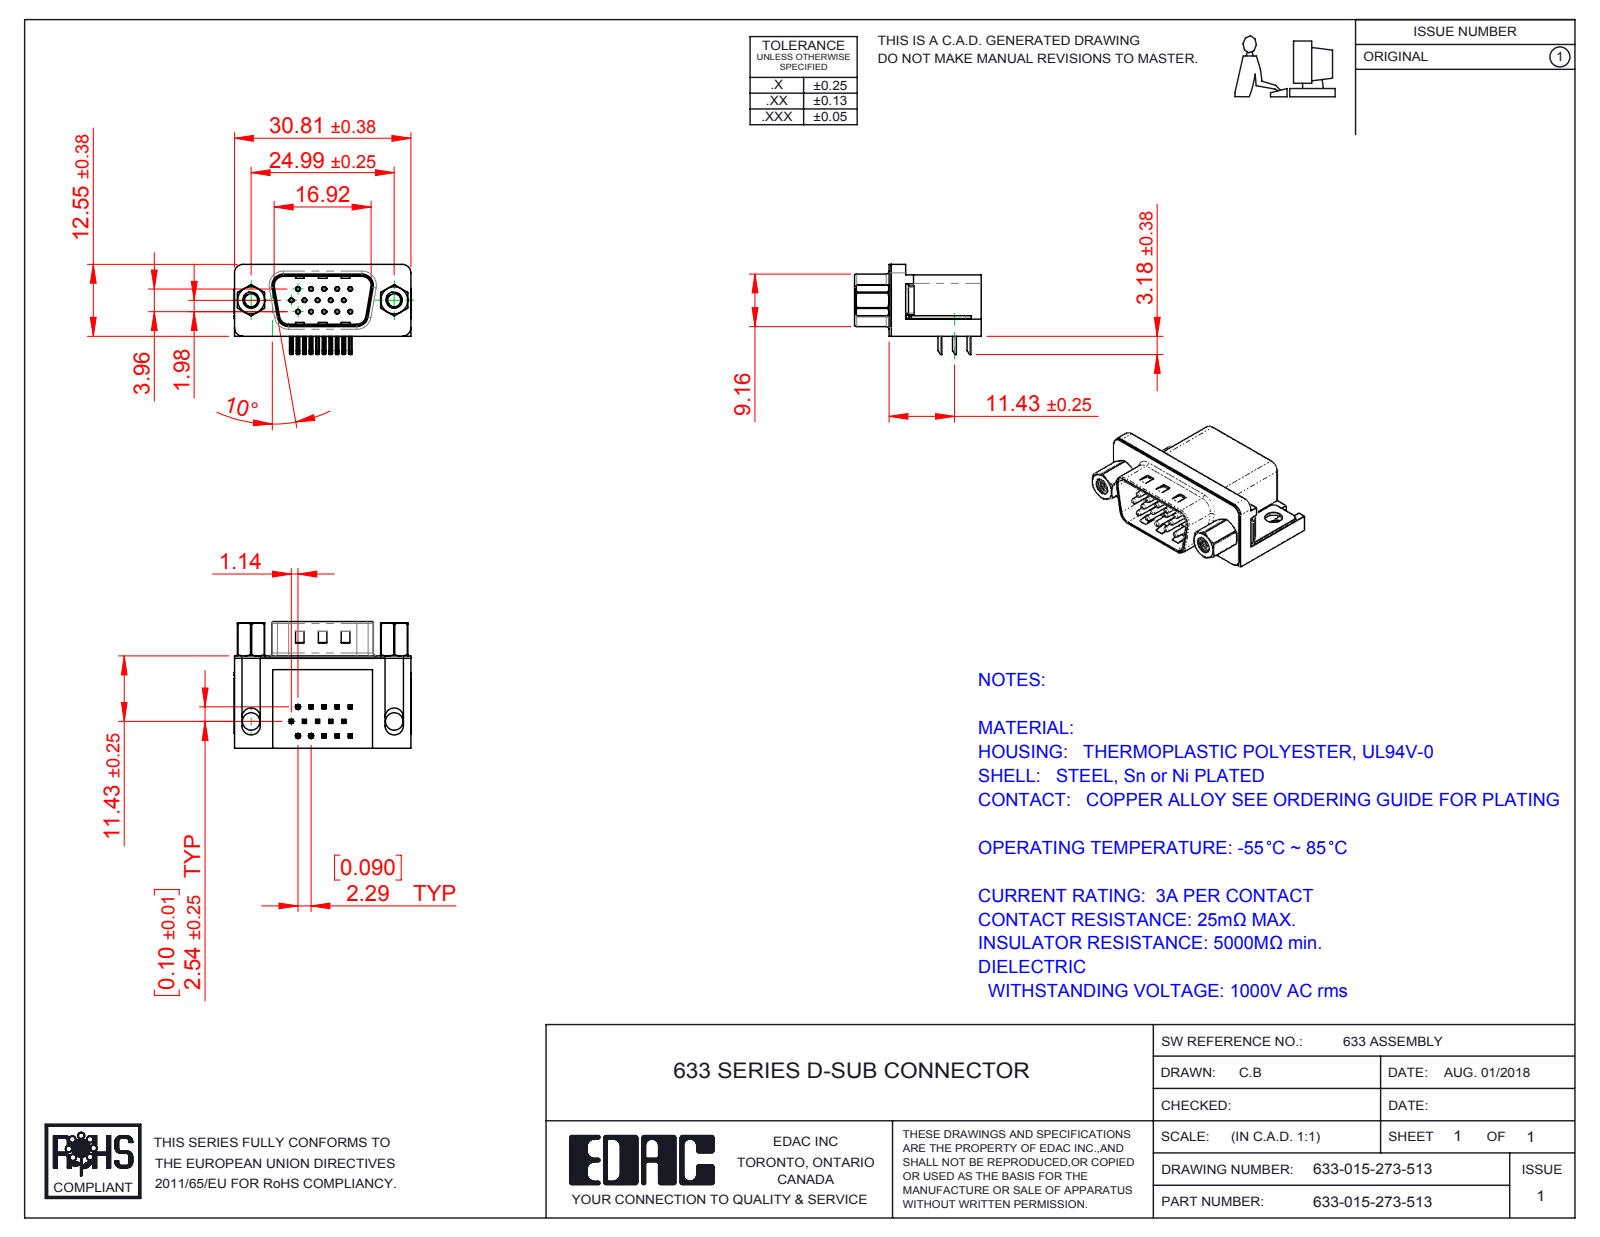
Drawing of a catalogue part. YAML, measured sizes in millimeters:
part_name: "633 Contact Bottom; 633 Shell_15 Contact; 633 Contact Middle; 633 4-40 Threaded Rivet (+6 more)"
step_written_by: "SolidWorks 2016 (CONFIG_CONTROL_DESIGN)"
units: millimeters
bodies: {solids: 23, faces: 1561, planar: 881, cylindrical: 507, other: 173}
overall_size: [30.89, 22.1, 15.73]
volume: 4273
surface_area: 5862
round_holes:
  - {diameter: 0.35, count: 15}
  - {diameter: 0.8, count: 15}
  - {diameter: 2.26, count: 2}
  - {diameter: 2.29, count: 2}
  - {diameter: 3.05, count: 2}
  - {diameter: 4, count: 2}
  - {diameter: 4.8, count: 2}
  - {diameter: 5, count: 2}
round_bosses_or_shafts:
  - {diameter: 0.75, count: 15}
  - {diameter: 4.9, count: 2}
  - {diameter: 4.75, count: 2}
  - {diameter: 3.9, count: 2}
  - {diameter: 2.79, count: 2}
partial_cylinders:
  - {radius: 0.25, count: 68}
  - {radius: 0.12, count: 30}
  - {radius: 1, count: 16}
  - {radius: 0.5, count: 9}
  - {radius: 1.6, count: 8}
  - {radius: 1.5, count: 7}
  - {radius: 0.9, count: 4}
  - {radius: 2, count: 4}
face_to_face_distances: [0.4, 10.35, 15.7, 16.1, 2.9, 0.5, 2.5, 6.7, 0.35, 10.7]
hole_center_spacings: [3.96, 2.28, 4.57, 2.29, 6.05, 6.86, 7.92, 6.04]
